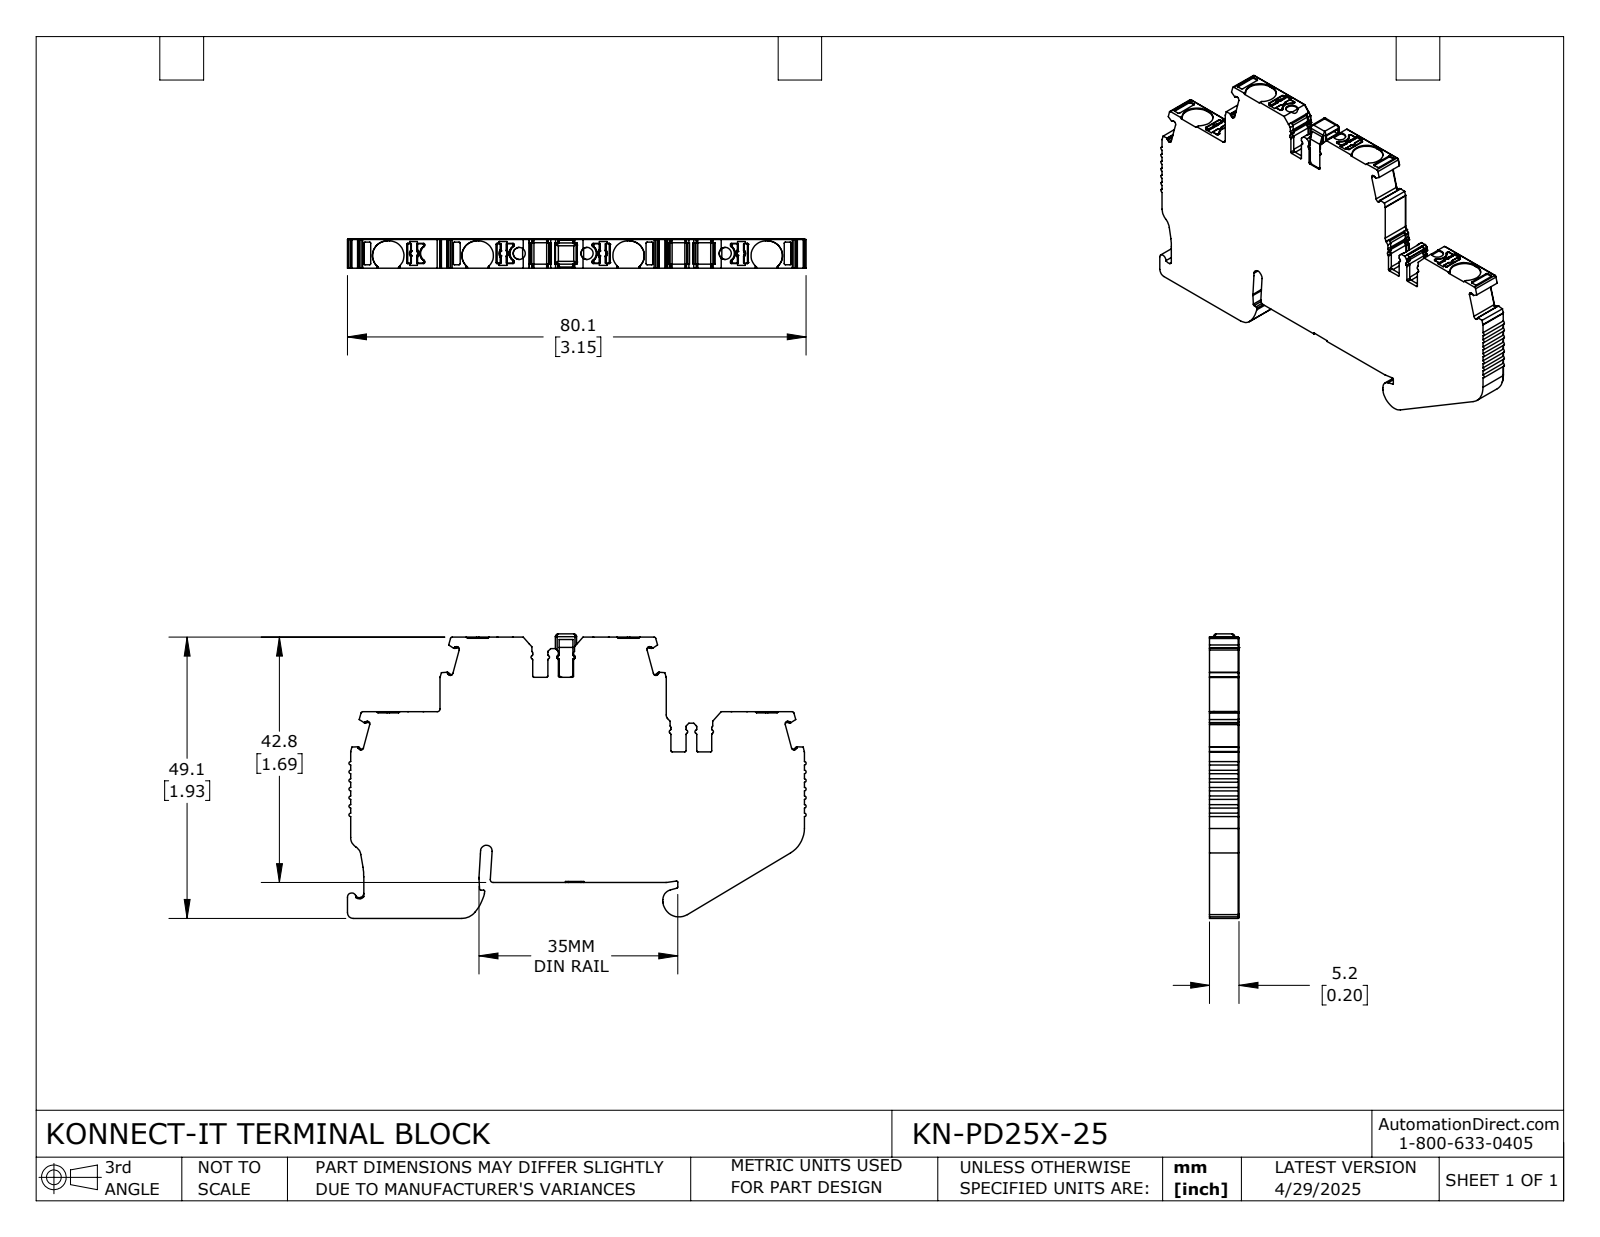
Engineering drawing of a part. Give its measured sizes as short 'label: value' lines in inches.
name: KN-PD25X-25
written by: SolidWorks 2024 (CONFIG_CONTROL_DESIGN)
unit: in
bodies: 1 solid, 1081 faces (529 planar, 475 cylindrical, 77 other)
size: 3.153 × 1.956 × 0.203
volume: 0.895 in³; area: 11.78 in²
holes: 3× ⌀0.083
rounds: 104× R0.008, 61× R0.012, 41× R0.004, 29× R0.02, 17× R0.016, 16× R0.006, 9× R0.024, 8× R0.006
face distances: 0.203, 0.512, 0.246, 1.678, 0.079, 1.166, 1.924, 1.412, 0.504, 1.42
hole spacings: 0.466, 0.95, 1.417
